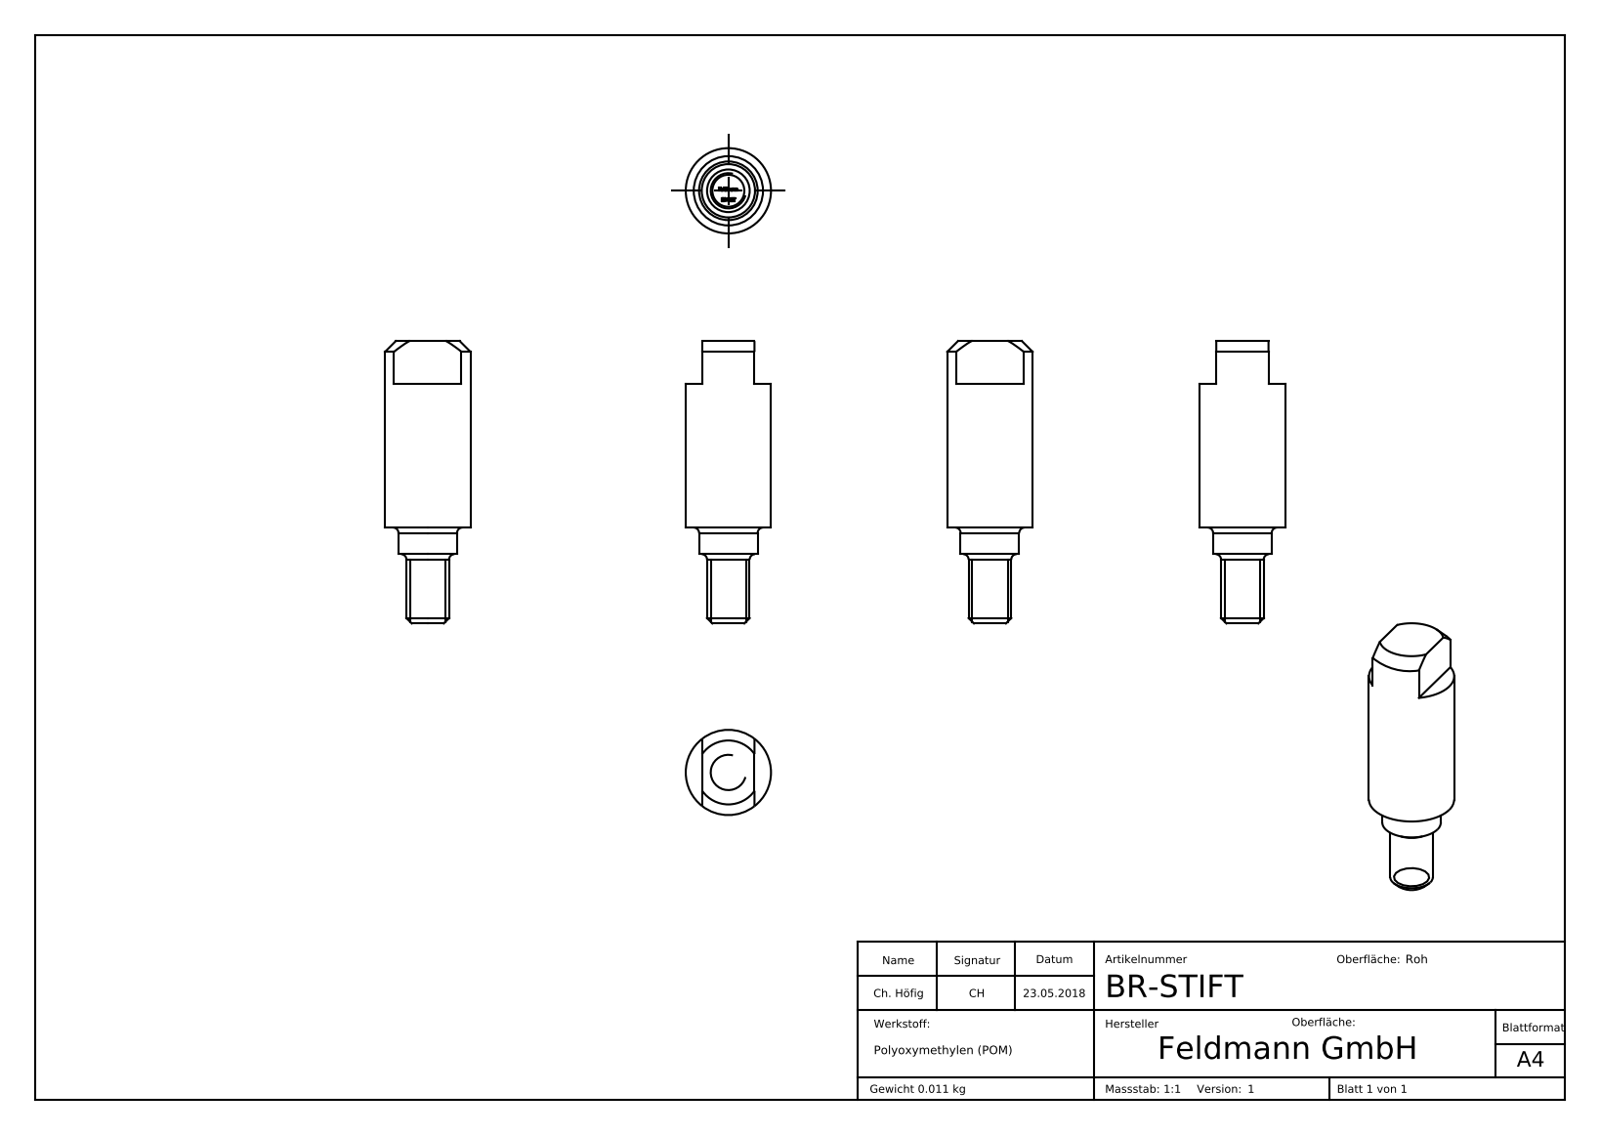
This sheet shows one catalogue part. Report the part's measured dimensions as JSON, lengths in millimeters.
{"part_name": "BR-STIFT", "step_written_by": "SolidWorks 2015 (CONFIG_CONTROL_DESIGN)", "units": "millimeters", "bodies": {"solids": 1, "faces": 231, "planar": 140, "cylindrical": 6, "other": 85}, "overall_size": [53, 16, 16], "volume_mm3": 7687, "surface_area_mm2": 2558, "round_bosses_or_shafts": [[16, 1], [11, 1], [8, 1]], "face_to_face_distances": [9.8, 35, 27, 8, 18, 45, 53, 13, 5, 32]}
